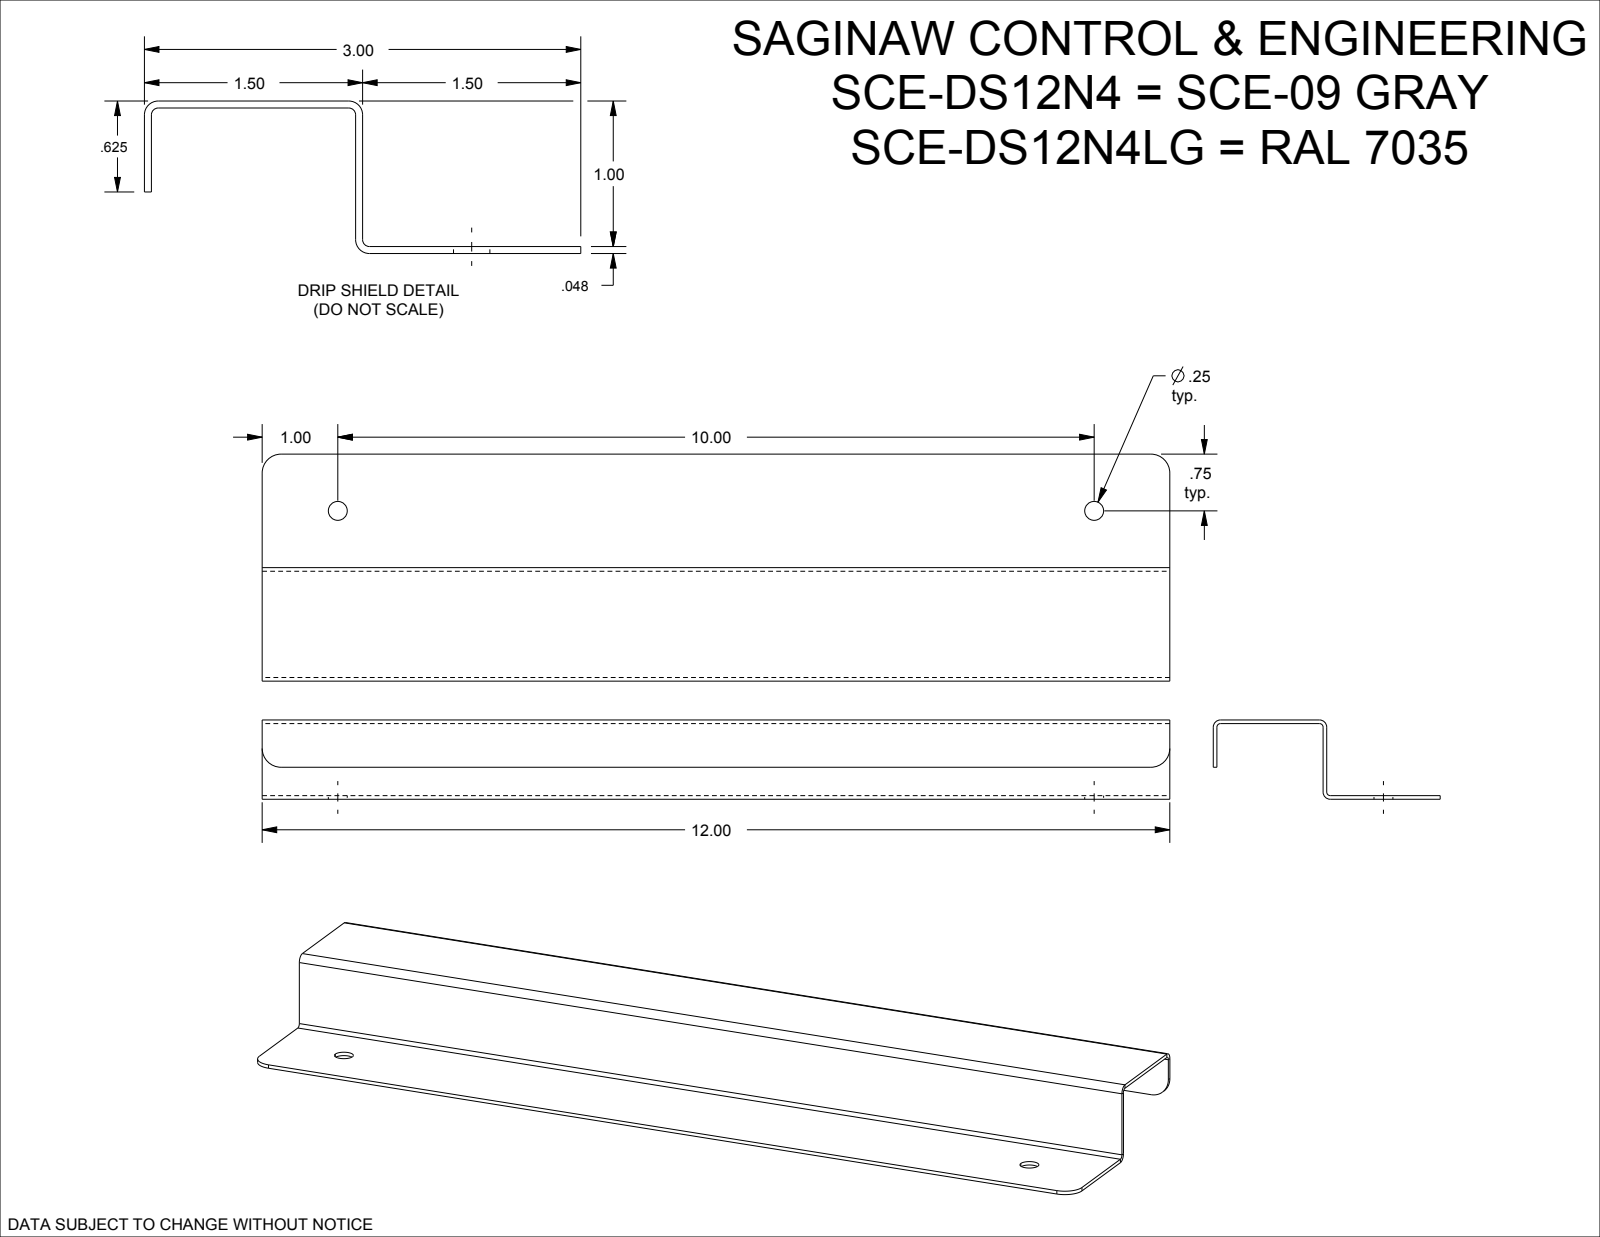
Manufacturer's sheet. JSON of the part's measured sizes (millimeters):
{"part_name": "SCE-DS12N4LG", "step_written_by": "SolidWorks 2019 (CONFIG_CONTROL_DESIGN)", "units": "millimeters", "bodies": {"solids": 1, "faces": 24, "planar": 12, "cylindrical": 12, "other": 0}, "overall_size": [304.8, 76.2, 26.6], "volume_mm3": 42210, "surface_area_mm2": 70320, "round_holes": [[6.4, 2]], "partial_cylinders_radius": [[6.4, 4], [1.2, 3], [2.4, 3]], "face_to_face_distances": [1.2, 25.4, 26.6, 24.2, 36.9, 38.1, 35.7, 10.7, 9.5, 14.7], "hole_center_spacings": [254]}
